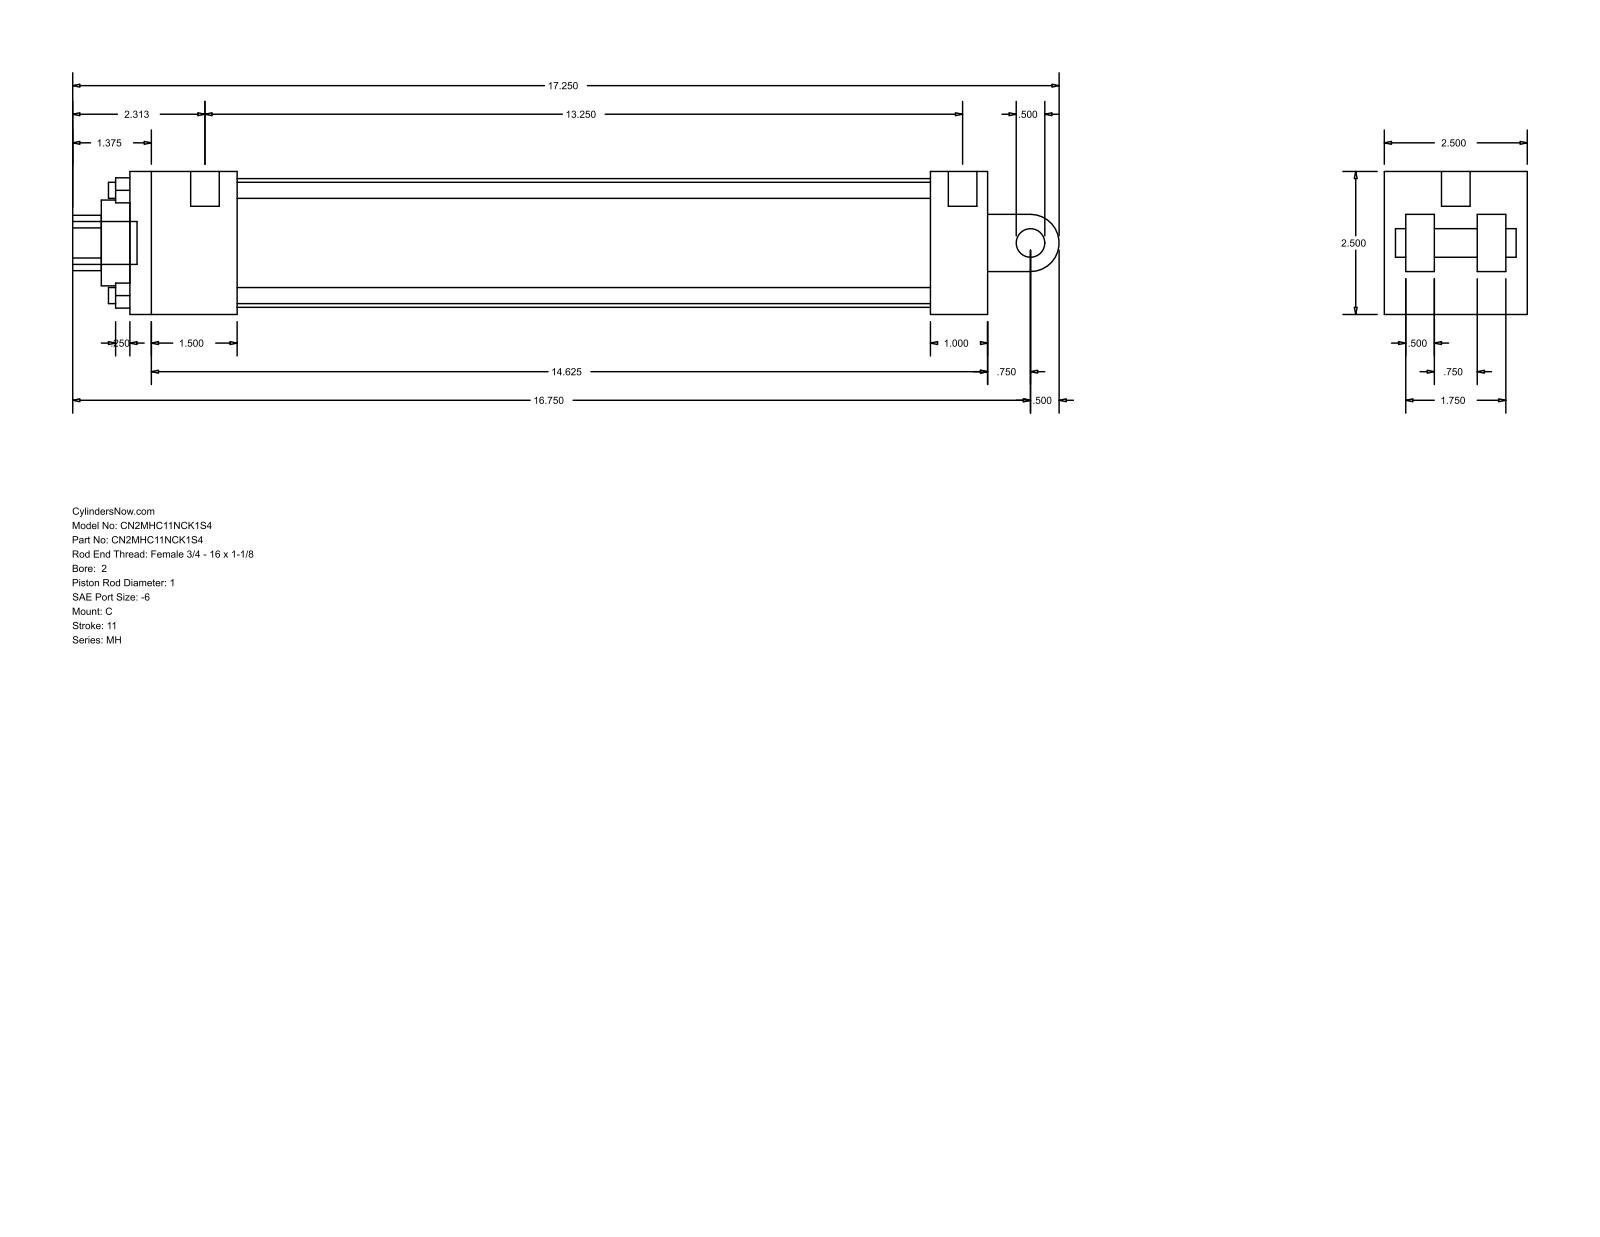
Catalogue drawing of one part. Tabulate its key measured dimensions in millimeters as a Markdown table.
| quantity | value |
| --- | --- |
| part name | MH_C__0200_1 |
| STEP written by | GSSL Pune (CONFIG_CONTROL_DESIGN) |
| units | millimeters |
| bodies | 0 solids, 99 faces (70 planar, 29 cylindrical, 0 other) |
| overall size | 438.15 × 63.5 × 63.5 |
| round holes (diameter × count) | 7.14 × 4, 5.56 × 2, 12.7 × 1, 25.4 × 1, 38.1 × 1, 57.15 × 1 |
| round bosses / shafts (diameter × count) | 12.7 × 2, 5.56 × 2, 19.05 × 1 |
| partial cylindrical surfaces (radius × count) | 12.29 × 1, 12.7 × 1 |
| main face-to-face distances | 63.5, 381, 12.7, 25.4, 9.52, 47.63, 53.98, 355.6, 307.97, 333.37 |
| hole center spacings | 33.05, 46.74, 66.1, 3.17 |
